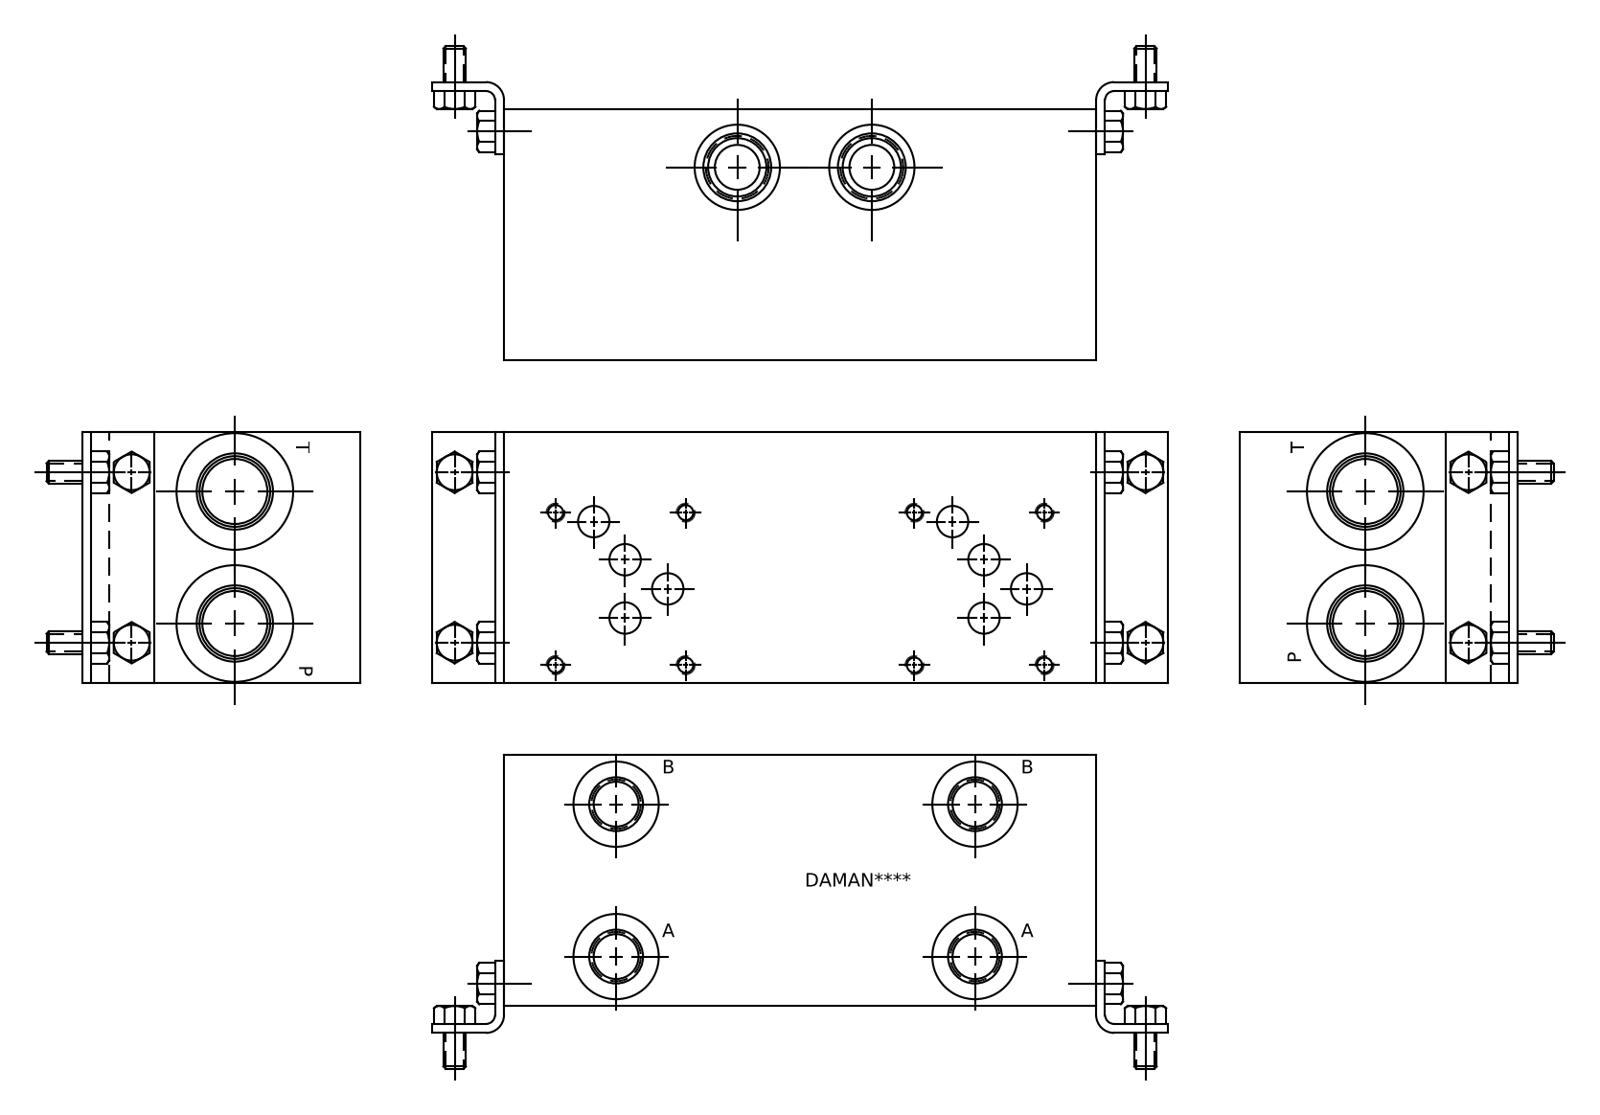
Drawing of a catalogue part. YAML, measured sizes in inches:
part_name: "C:\\\\Program Files\\\\PARO\\\\Hydroman 800\\\\Export\\\\AD05P025S_CPAD"
step_written_by: "Autodesk Inventor 2012 (AUTOMOTIVE_DESIGN)"
units: inches
bodies: {solids: 1, faces: 130, planar: 26, cylindrical: 62, other: 42}
overall_size: [8.25, 3.5, 3.5]
volume: 93.43
surface_area: 179
round_holes:
  - {diameter: 0.201, count: 8}
  - {diameter: 0.438, count: 8}
  - {diameter: 0.689, count: 4}
  - {diameter: 0.811, count: 4}
  - {diameter: 1.191, count: 4}
  - {diameter: 0.257, count: 2}
  - {diameter: 0.563, count: 2}
  - {diameter: 0.625, count: 2}
  - {diameter: 0.625, count: 2}
  - {diameter: 0.626, count: 2}
  - {diameter: 0.812, count: 2}
  - {diameter: 0.906, count: 2}
face_to_face_distances: [3.5, 8.25, 0.031, 8.219, 3.469, 8.188, 0.16, 8.09, 0.129, 8.059]
hole_center_spacings: [5, 1.813, 0.546, 0.719, 0.812, 1.069, 1.171, 1.394]
